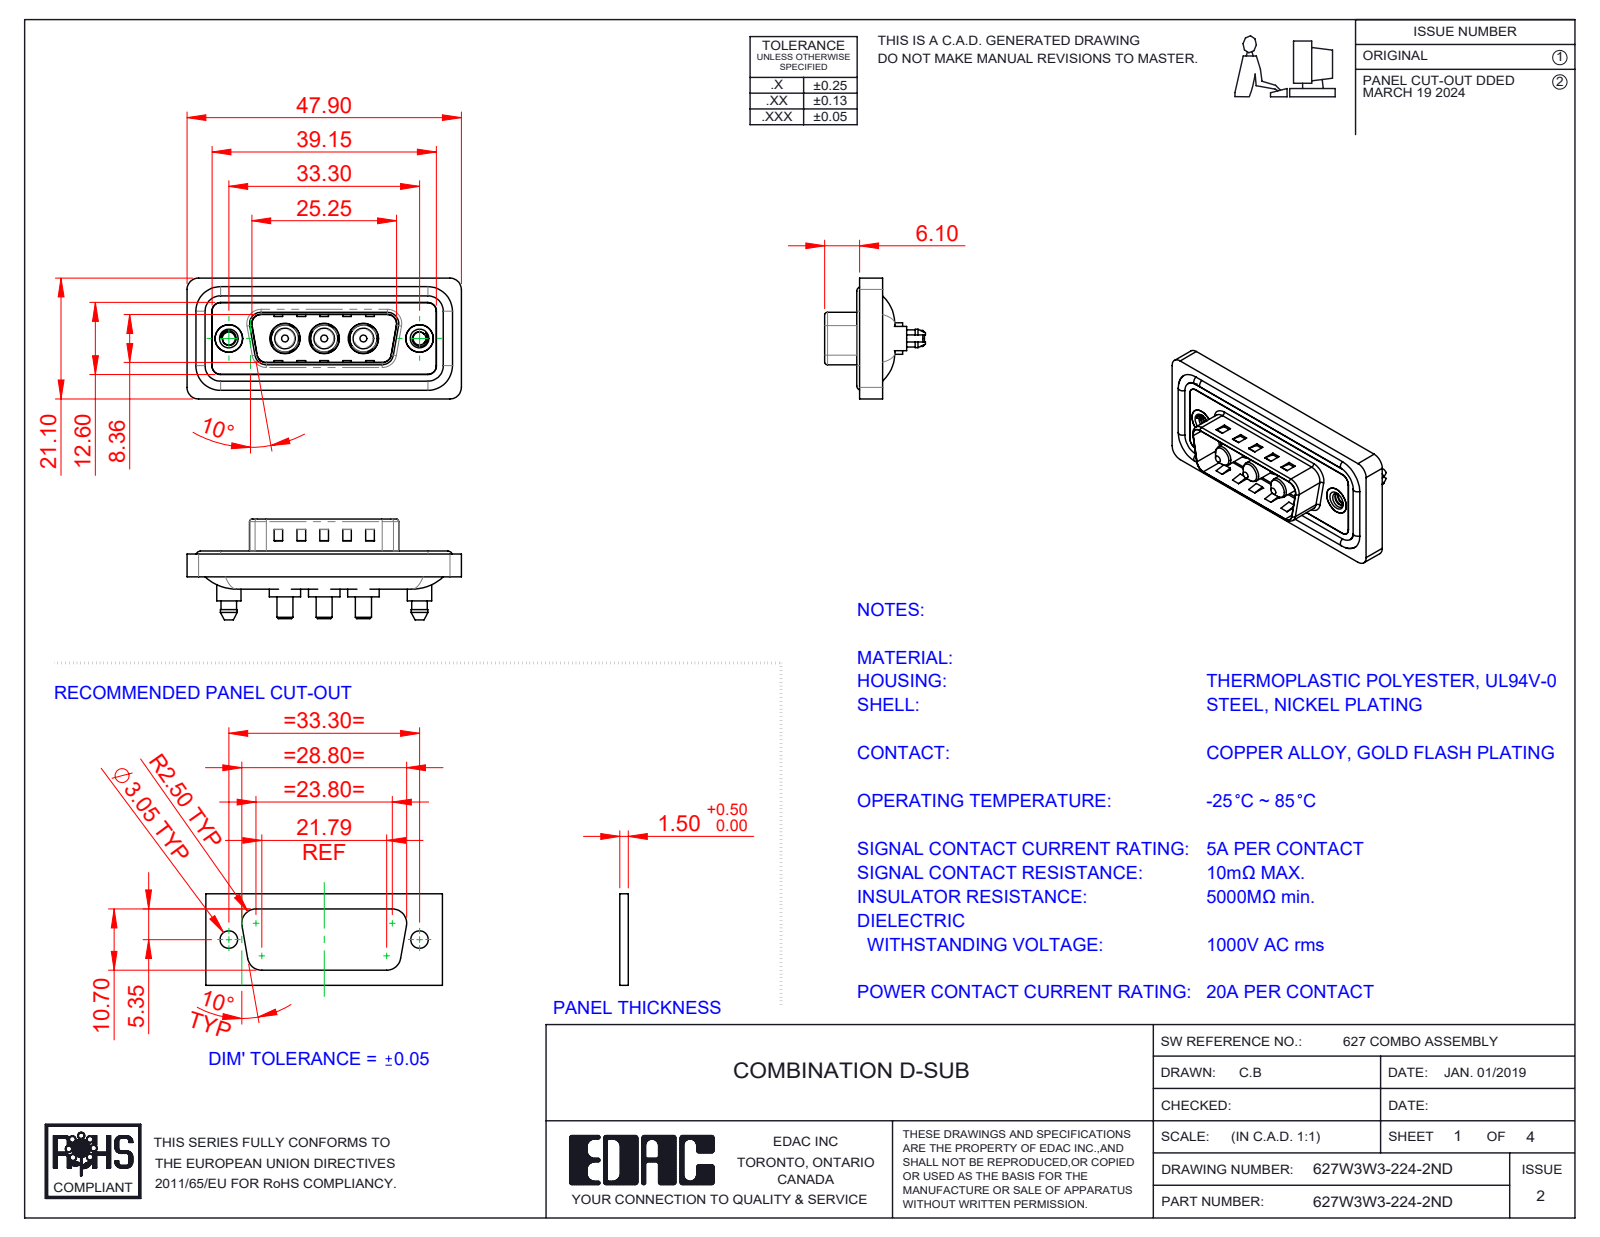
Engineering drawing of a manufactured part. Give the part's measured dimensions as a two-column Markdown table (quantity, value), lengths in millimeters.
| quantity | value |
| --- | --- |
| part name | 627Combo Threaded Boardlock_D; 627W3W3-224-2ND; 627Combo Housing_3W3; Power Pin_20A S (+4 more) |
| STEP written by | SolidWorks 2023 (CONFIG_CONTROL_DESIGN) |
| units | millimeters |
| bodies | 13 solids, 622 faces (223 planar, 281 cylindrical, 118 other) |
| overall size | 47.9 × 21.1 × 17.6 |
| volume | 5 720 mm³ |
| surface area | 9 090 mm² |
| round holes (diameter × count) | 4.85 × 3, 5.3 × 3, 2.26 × 2, 4 × 2, 4.8 × 2, 5 × 2 |
| round bosses / shafts (diameter × count) | 1.6 × 4, 5.5 × 3, 5.2 × 3, 4.75 × 3, 3.75 × 3, 3.6 × 3, 2.8 × 3, 5.4 × 2 |
| partial cylindrical surfaces (radius × count) | 1.5 × 28, 2 × 20, 1.6 × 10, 0.5 × 8, 0.25 × 4, 0.6 × 4, 0.65 × 4, 0.9 × 4 |
| main face-to-face distances | 0.4, 1.1, 1.5, 3.1, 1.6, 0.5, 2.9, 4, 0.7, 0.82 |
| hole center spacings | 6.85, 9.8, 16.65, 23.5, 13.7, 33.3 |
